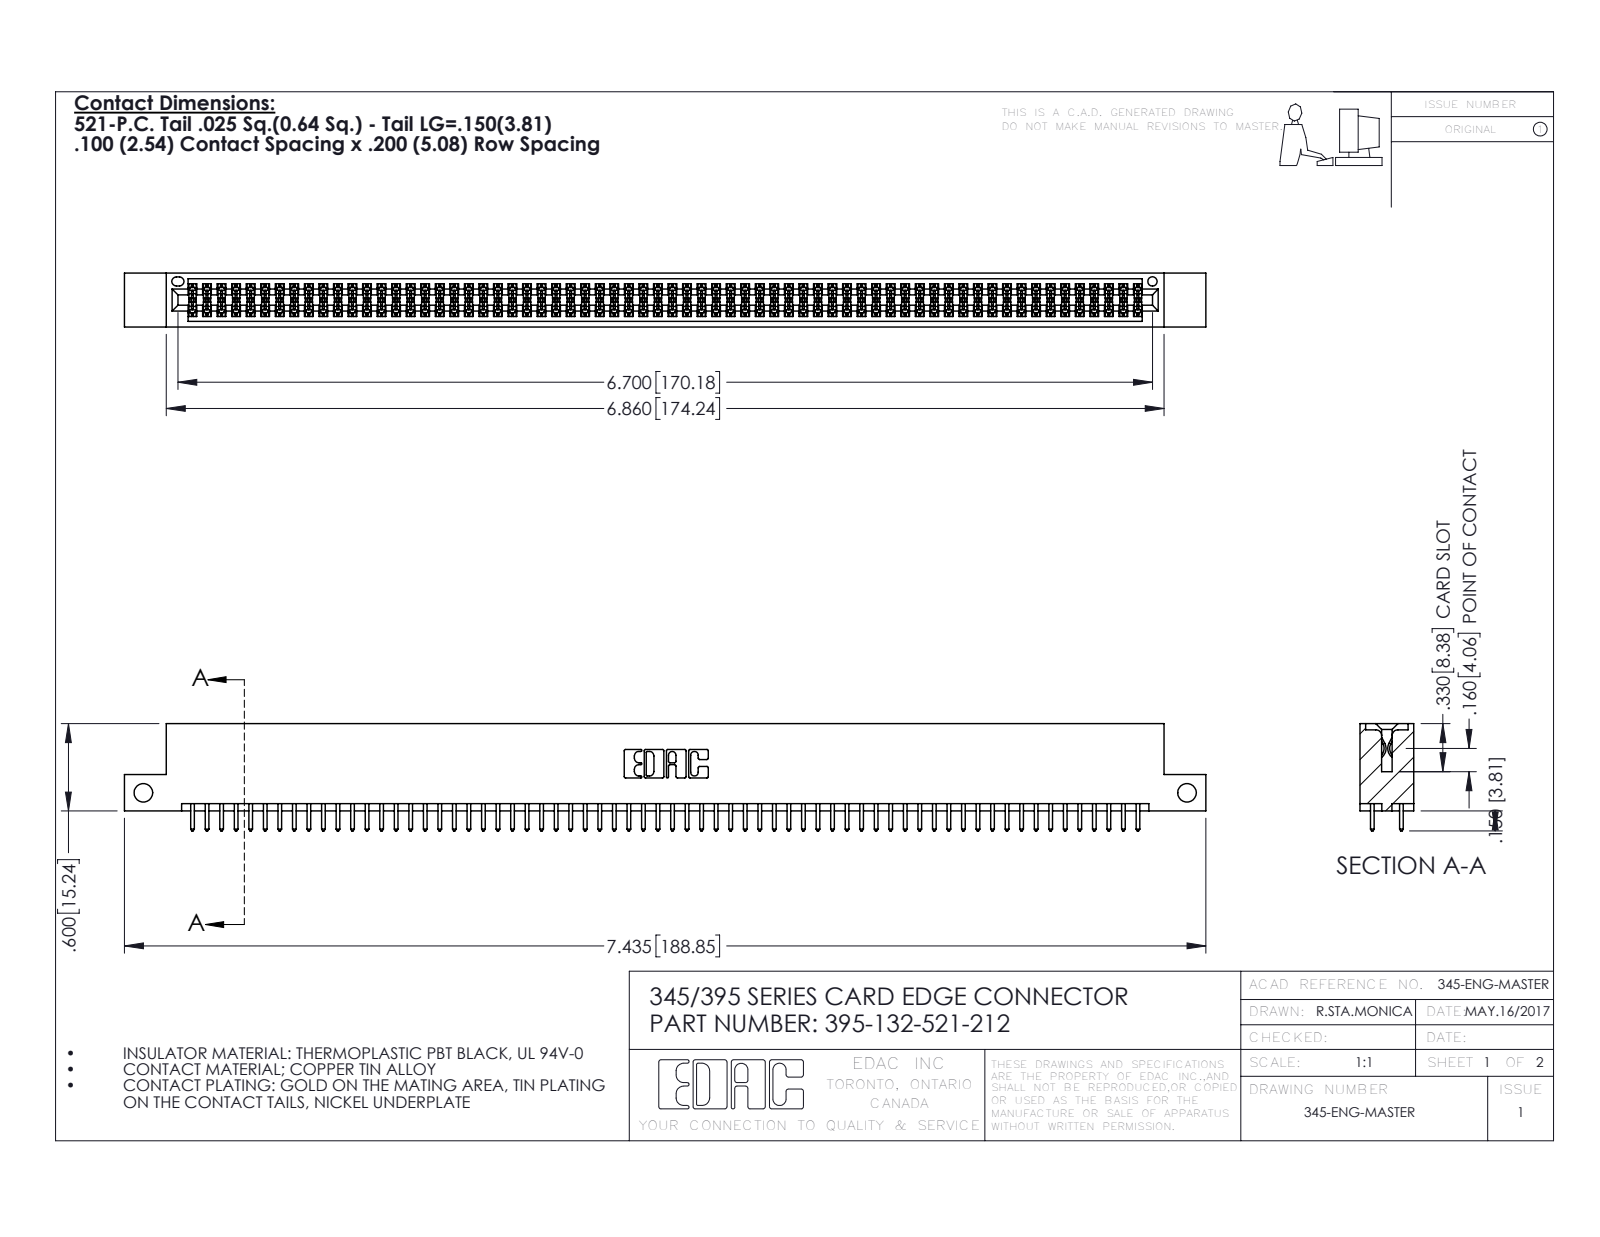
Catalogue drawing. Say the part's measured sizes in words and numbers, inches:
The part is named "345-292-001_345-293-121; 345 Part_Flush Mounting Lugs - Side Mount; 395-132-521-212". Its 3-D file was written by "SolidWorks 2016 (CONFIG_CONTROL_DESIGN)". It is 133 solids with 6726 faces: 4436 planar, 2290 cylindrical and 0 other. Overall it measures 7.435 by 0.737 by 0.37 inches. Its volume is 1.124 cubic inches and its surface area 42.19 square inches. Round holes: 2 of diameter 0.128, 1 of diameter 0.064. Partial cylindrical surfaces (rounded edges, fillets, slot ends): 198 of radius 0.006, 132 of radius 0.01, 22 of radius 0.01, 6 of radius 0.007, 6 of radius 0.031, 3 of radius 0.026, 2 of radius 0.014, 2 of radius 0.019. The main face-to-face distances are 0.298, 0.072, 0.2, 0.098, 0.272, 0.025, 0.37, 0.225, 0.175, 0.149. The hole center spacings are 7.175.
